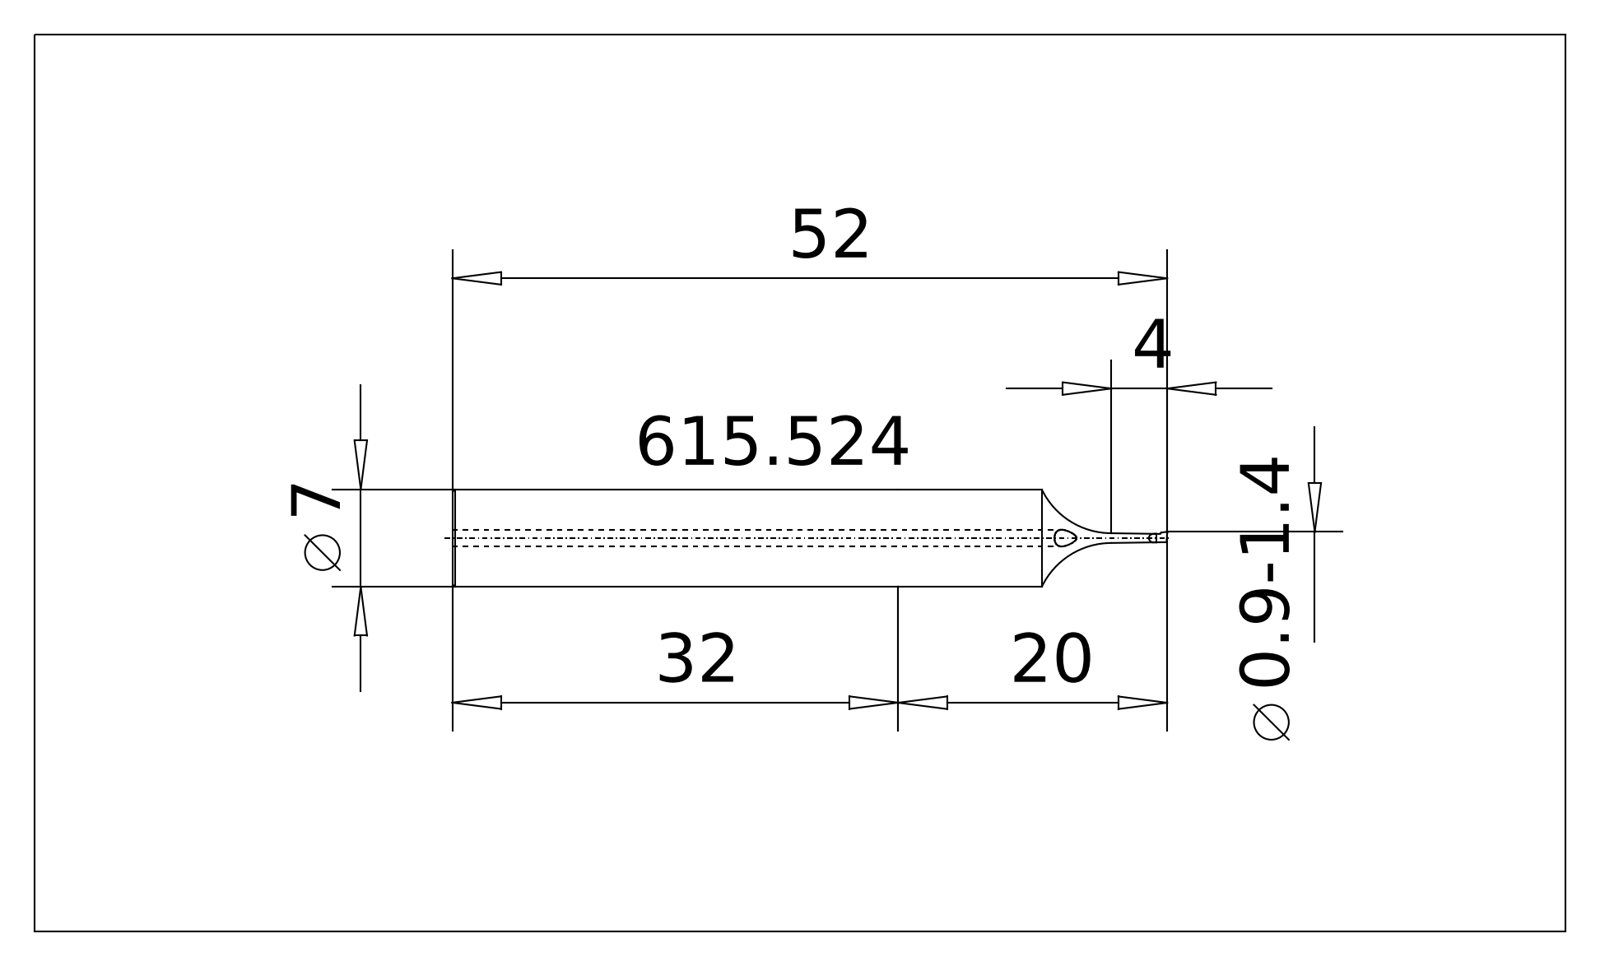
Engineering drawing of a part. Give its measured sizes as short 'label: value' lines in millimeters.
written by: ACIS (automotive_design)
unit: mm
bodies: 1 solid, 25 faces (8 planar, 5 cylindrical, 12 other)
size: 51.3 × 7 × 7
volume: 1 502 mm³; area: 1 122 mm²
holes: 1× ⌀1.2
bosses: 1× ⌀7
rounds: 1× R0.5
face distances: 37
